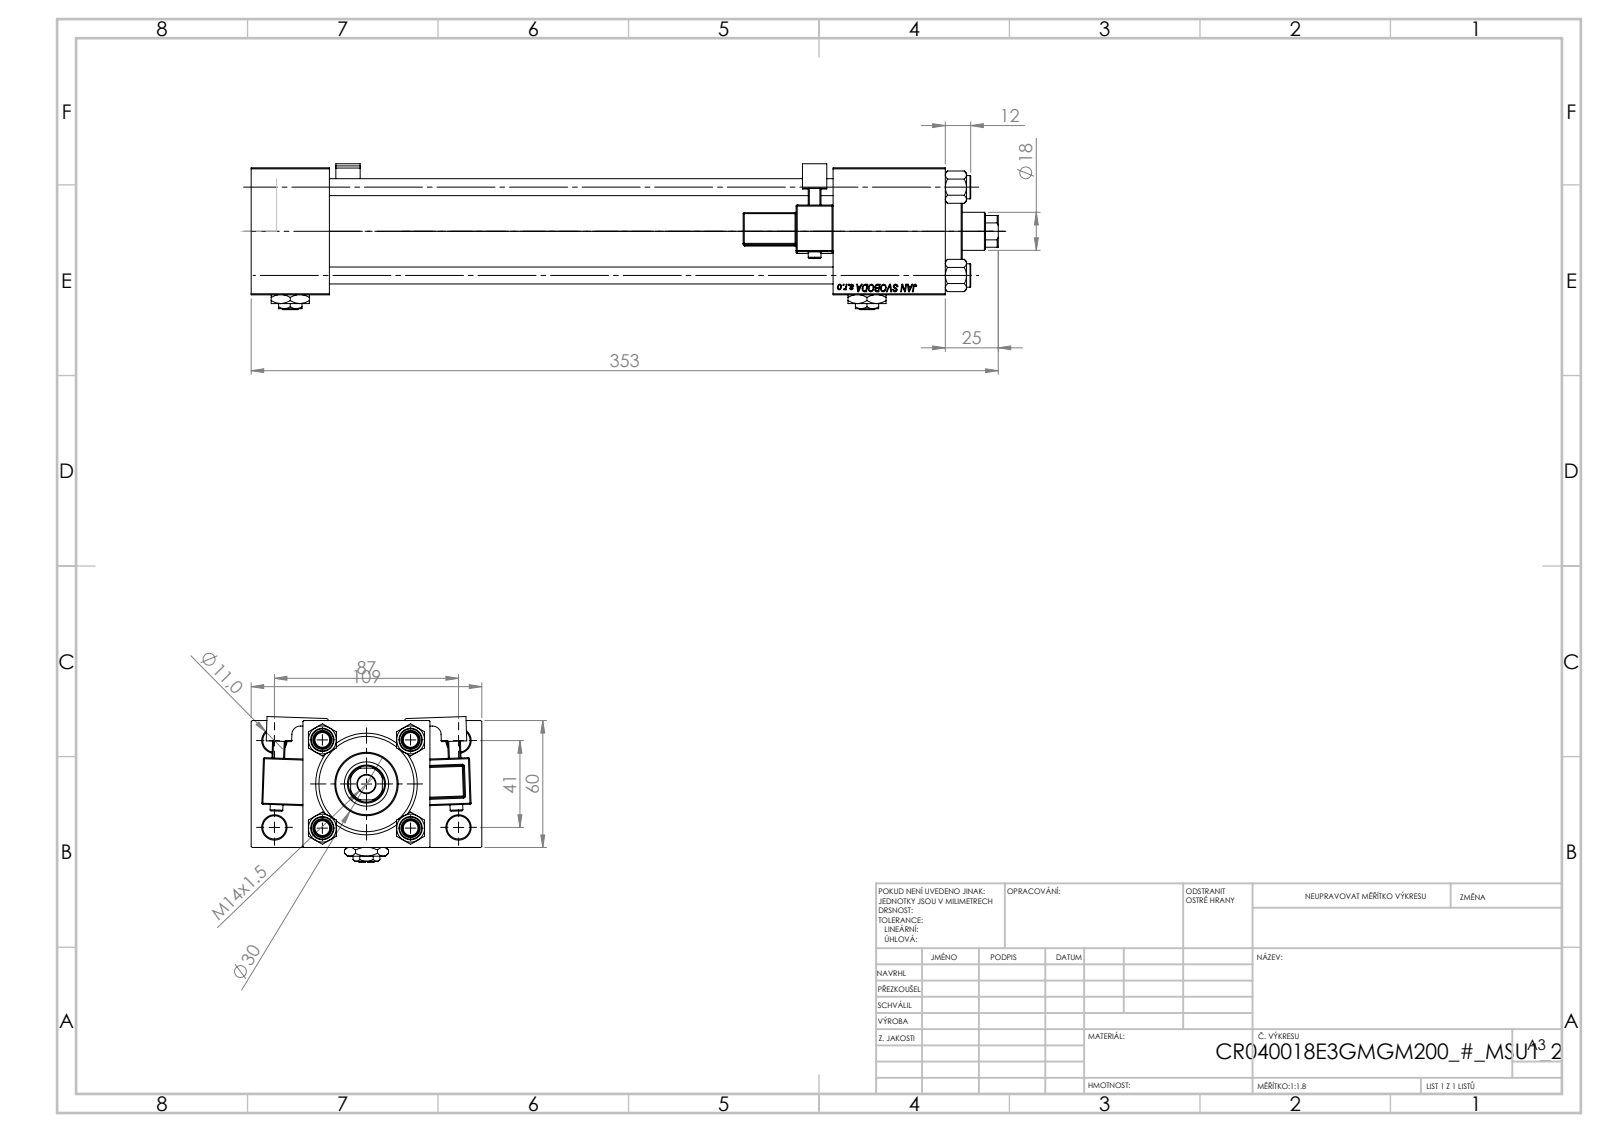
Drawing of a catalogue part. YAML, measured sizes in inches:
part_name: "Zatka_pro_OIL_PORT; V215CR_MSU; V215CR_E_Body; V215CR_VCP_E (+3 more)"
step_written_by: "SolidWorks 2019 (CONFIG_CONTROL_DESIGN)"
units: inches
bodies: {solids: 15, faces: 1391, planar: 604, cylindrical: 157, other: 630}
overall_size: [13.898, 4.291, 2.713]
volume: 42.23
surface_area: 335.4
round_holes:
  - {diameter: 0.315, count: 4}
  - {diameter: 0.433, count: 4}
  - {diameter: 0.656, count: 4}
  - {diameter: 0.945, count: 4}
  - {diameter: 0.276, count: 3}
  - {diameter: 0.335, count: 1}
  - {diameter: 0.709, count: 1}
  - {diameter: 0.827, count: 1}
  - {diameter: 1.22, count: 1}
  - {diameter: 1.575, count: 1}
  - {diameter: 1.772, count: 1}
round_bosses_or_shafts:
  - {diameter: 0.433, count: 4}
  - {diameter: 0.236, count: 2}
  - {diameter: 1.811, count: 1}
  - {diameter: 1.181, count: 1}
partial_cylinders:
  - {radius: 0.02, count: 48}
  - {radius: 0.039, count: 2}
  - {radius: 0.098, count: 2}
  - {radius: 0.157, count: 2}
  - {radius: 0.335, count: 1}
face_to_face_distances: [2.362, 1.457, 0.965, 3.327, 2.087, 12.913, 11.457, 10.827, 9.37, 0.957]
hole_center_spacings: [0.892, 1.161, 1.642, 1.856, 1.893, 2.533, 3.011, 1.614]
